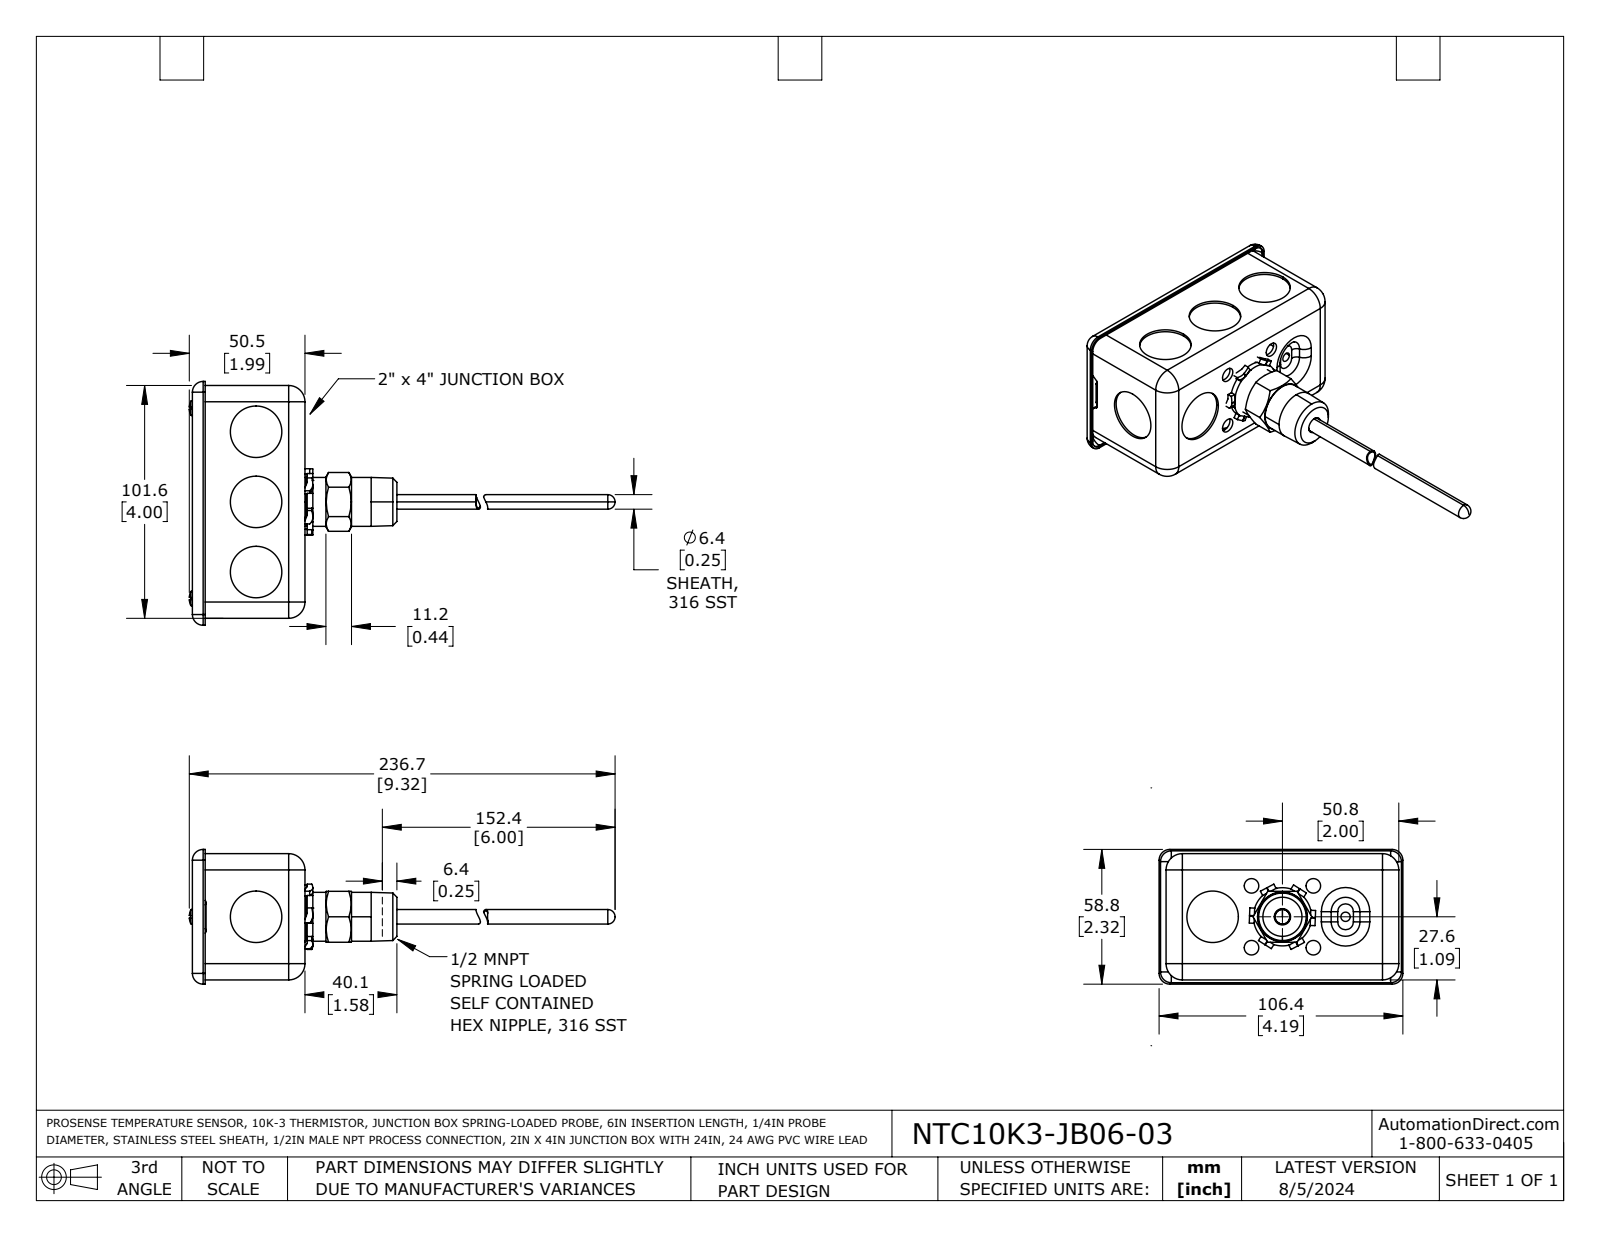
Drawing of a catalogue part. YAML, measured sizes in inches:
part_name: "NTC10K3-JB06-03"
step_written_by: "SolidWorks 2021 (AUTOMOTIVE_DESIGN)"
units: inches
bodies: {solids: 5, faces: 366, planar: 155, cylindrical: 147, other: 64}
overall_size: [9.313, 4.19, 2.315]
volume: 3.107
surface_area: 101.3
round_holes:
  - {diameter: 0.885, count: 6}
  - {diameter: 0.25, count: 4}
  - {diameter: 0.115, count: 2}
  - {diameter: 0.16, count: 1}
  - {diameter: 0.21, count: 1}
  - {diameter: 0.26, count: 1}
  - {diameter: 0.438, count: 1}
  - {diameter: 0.466, count: 1}
round_bosses_or_shafts:
  - {diameter: 0.136, count: 2}
  - {diameter: 0.84, count: 1}
  - {diameter: 0.25, count: 1}
partial_cylinders:
  - {radius: 0.185, count: 16}
  - {radius: 0.245, count: 8}
  - {radius: 0.28, count: 8}
  - {radius: 0.174, count: 6}
  - {radius: 0.555, count: 6}
  - {radius: 0.045, count: 4}
  - {radius: 0.165, count: 4}
  - {radius: 0.07, count: 2}
face_to_face_distances: [0.07, 0.03, 2.03, 2.1, 0.04, 0.1, 0.06, 1.855, 2.07, 2]
hole_center_spacings: [0.751, 1.062, 1.248, 2.254, 0.767, 0.854, 1.205, 1.502]
